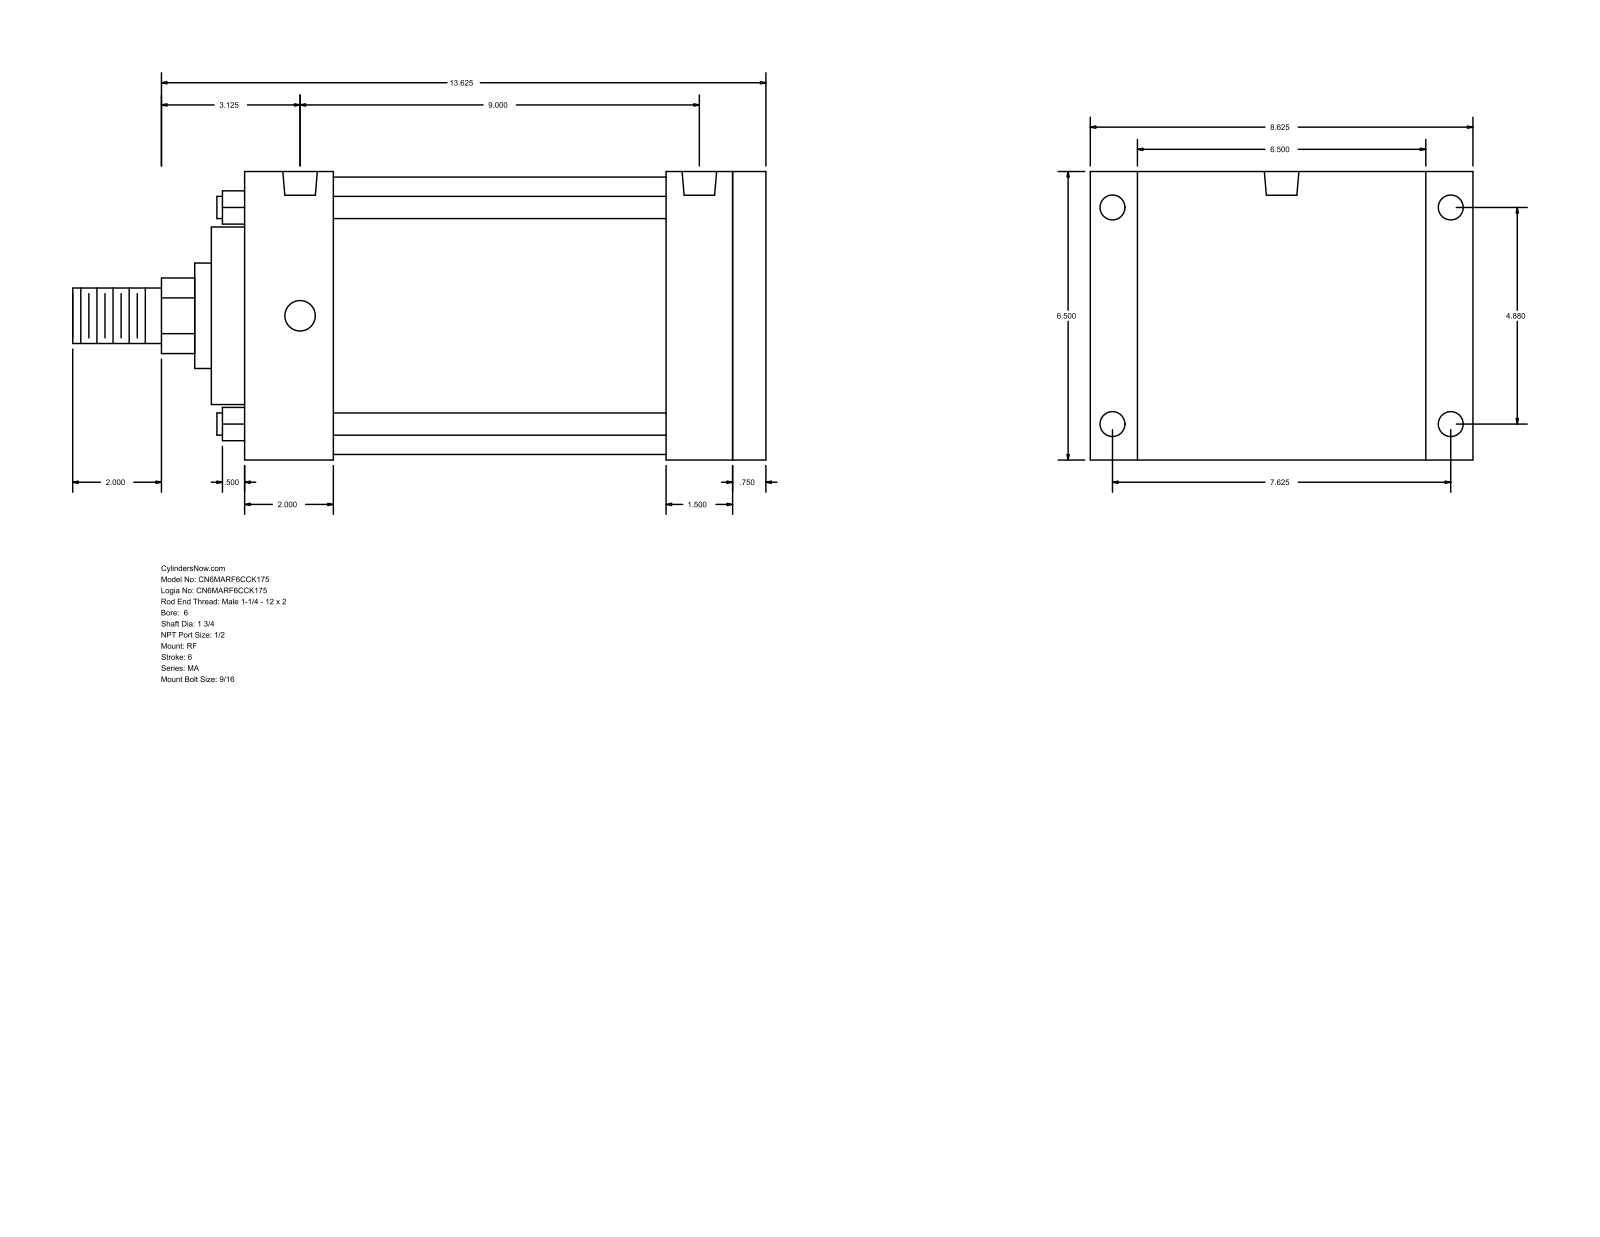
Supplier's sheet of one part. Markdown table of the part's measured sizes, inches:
| quantity | value |
| --- | --- |
| part name | MA_RF__0600_1.75 |
| STEP written by | GSSL Pune (CONFIG_CONTROL_DESIGN) |
| units | inches |
| bodies | 0 solids, 94 faces (65 planar, 29 cylindrical, 0 other) |
| overall size | 15.625 × 8.625 × 6.5 |
| round holes (diameter × count) | 0.563 × 4, 0.687 × 4, 0.778 × 2 |
| round bosses / shafts (diameter × count) | 0.5 × 4, 6.25 × 1, 4 × 1, 2.375 × 1, 1.75 × 1, 1.25 × 1 |
| partial cylindrical surfaces (radius × count) | 0.852 × 1 |
| main face-to-face distances | 6.5, 11.75, 0.75, 11, 2, 9, 9.75, 9.5, 7.5, 1.5 |
| hole center spacings | 4.88, 7.625, 9, 9.053 |
